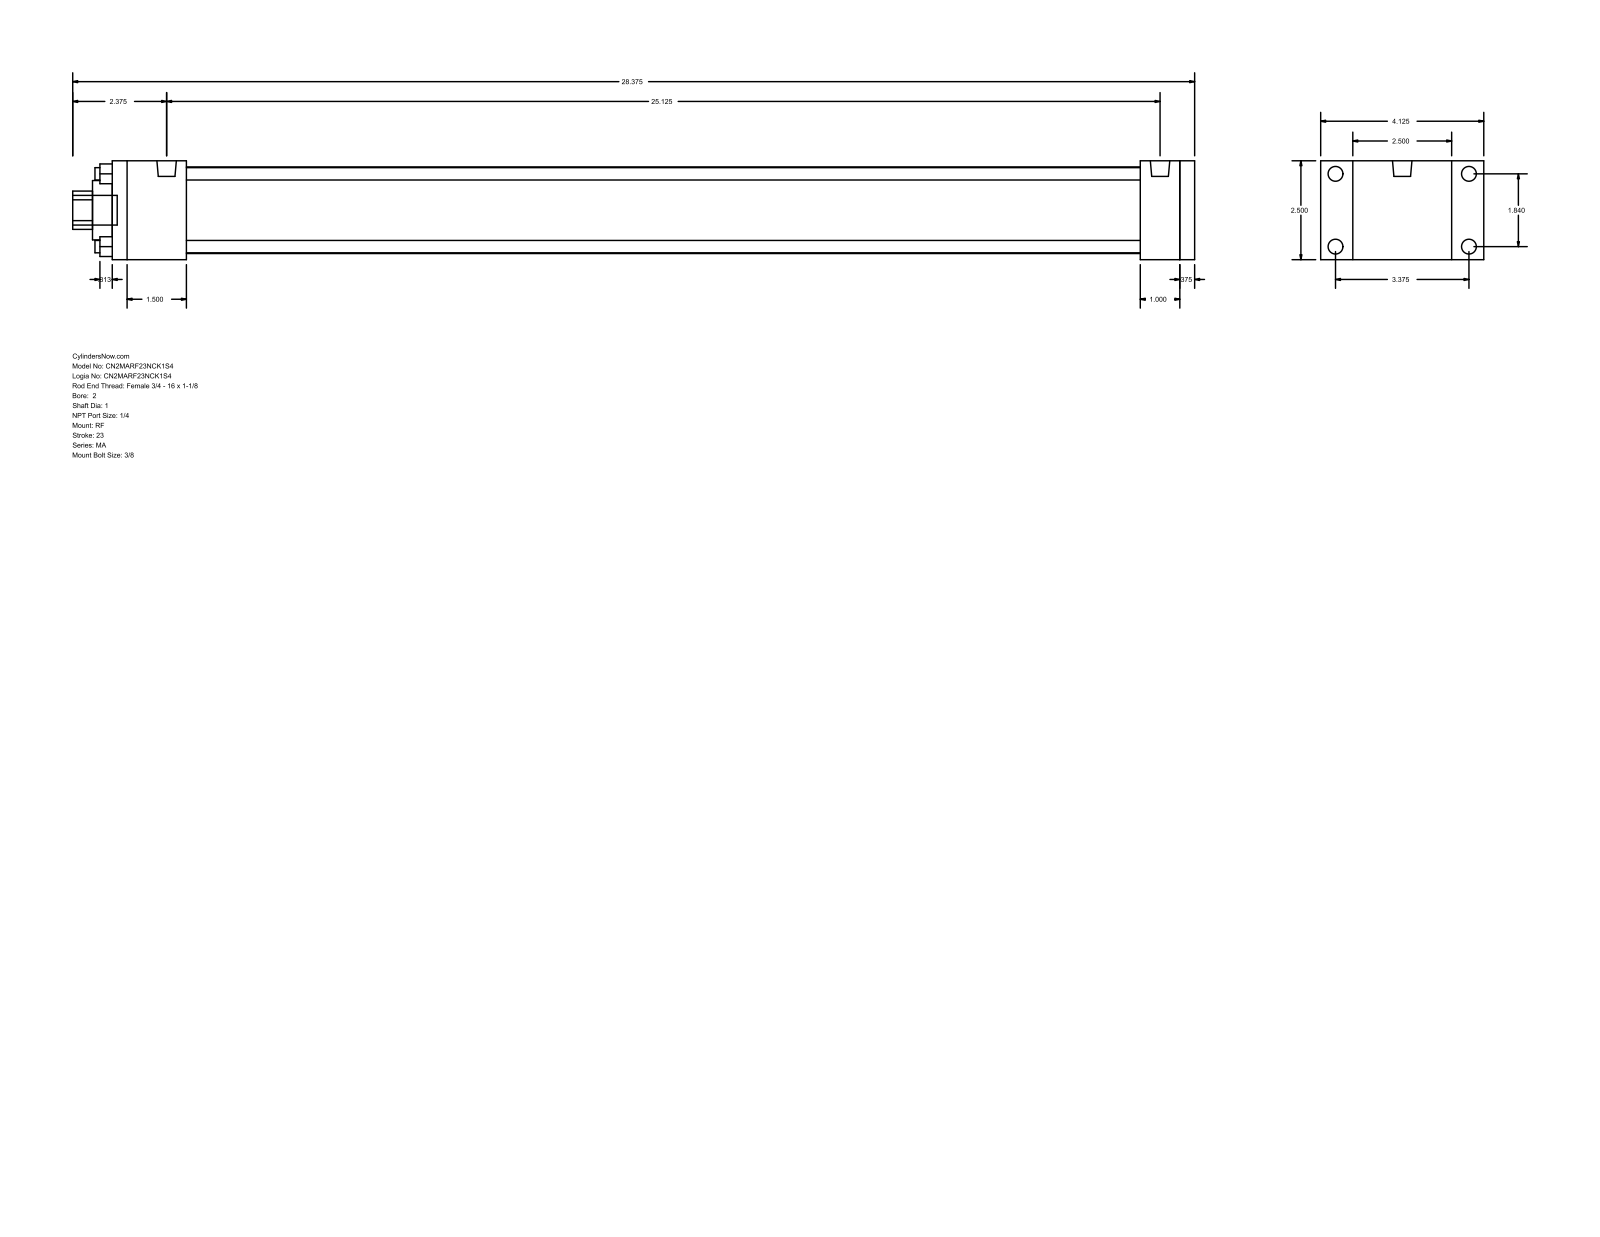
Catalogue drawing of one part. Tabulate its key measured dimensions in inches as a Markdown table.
| quantity | value |
| --- | --- |
| part name | MA_RF__0200_1 |
| STEP written by | GSSL Pune (CONFIG_CONTROL_DESIGN) |
| units | inches |
| bodies | 0 solids, 92 faces (64 planar, 28 cylindrical, 0 other) |
| overall size | 28.375 × 4.125 × 2.5 |
| round holes (diameter × count) | 0.313 × 4, 1 × 1, 1.5 × 1, 2.19 × 1 |
| round bosses / shafts (diameter × count) | 0.375 × 4, 0.313 × 4, 0.492 × 2, 0.75 × 1 |
| partial cylindrical surfaces (radius × count) | 0.484 × 1 |
| main face-to-face distances | 2.5, 27, 0.375, 27.375, 1, 0.813, 0.5, 1.875, 25.125, 25.5 |
| hole center spacings | 1.301, 1.84, 2.602 |
